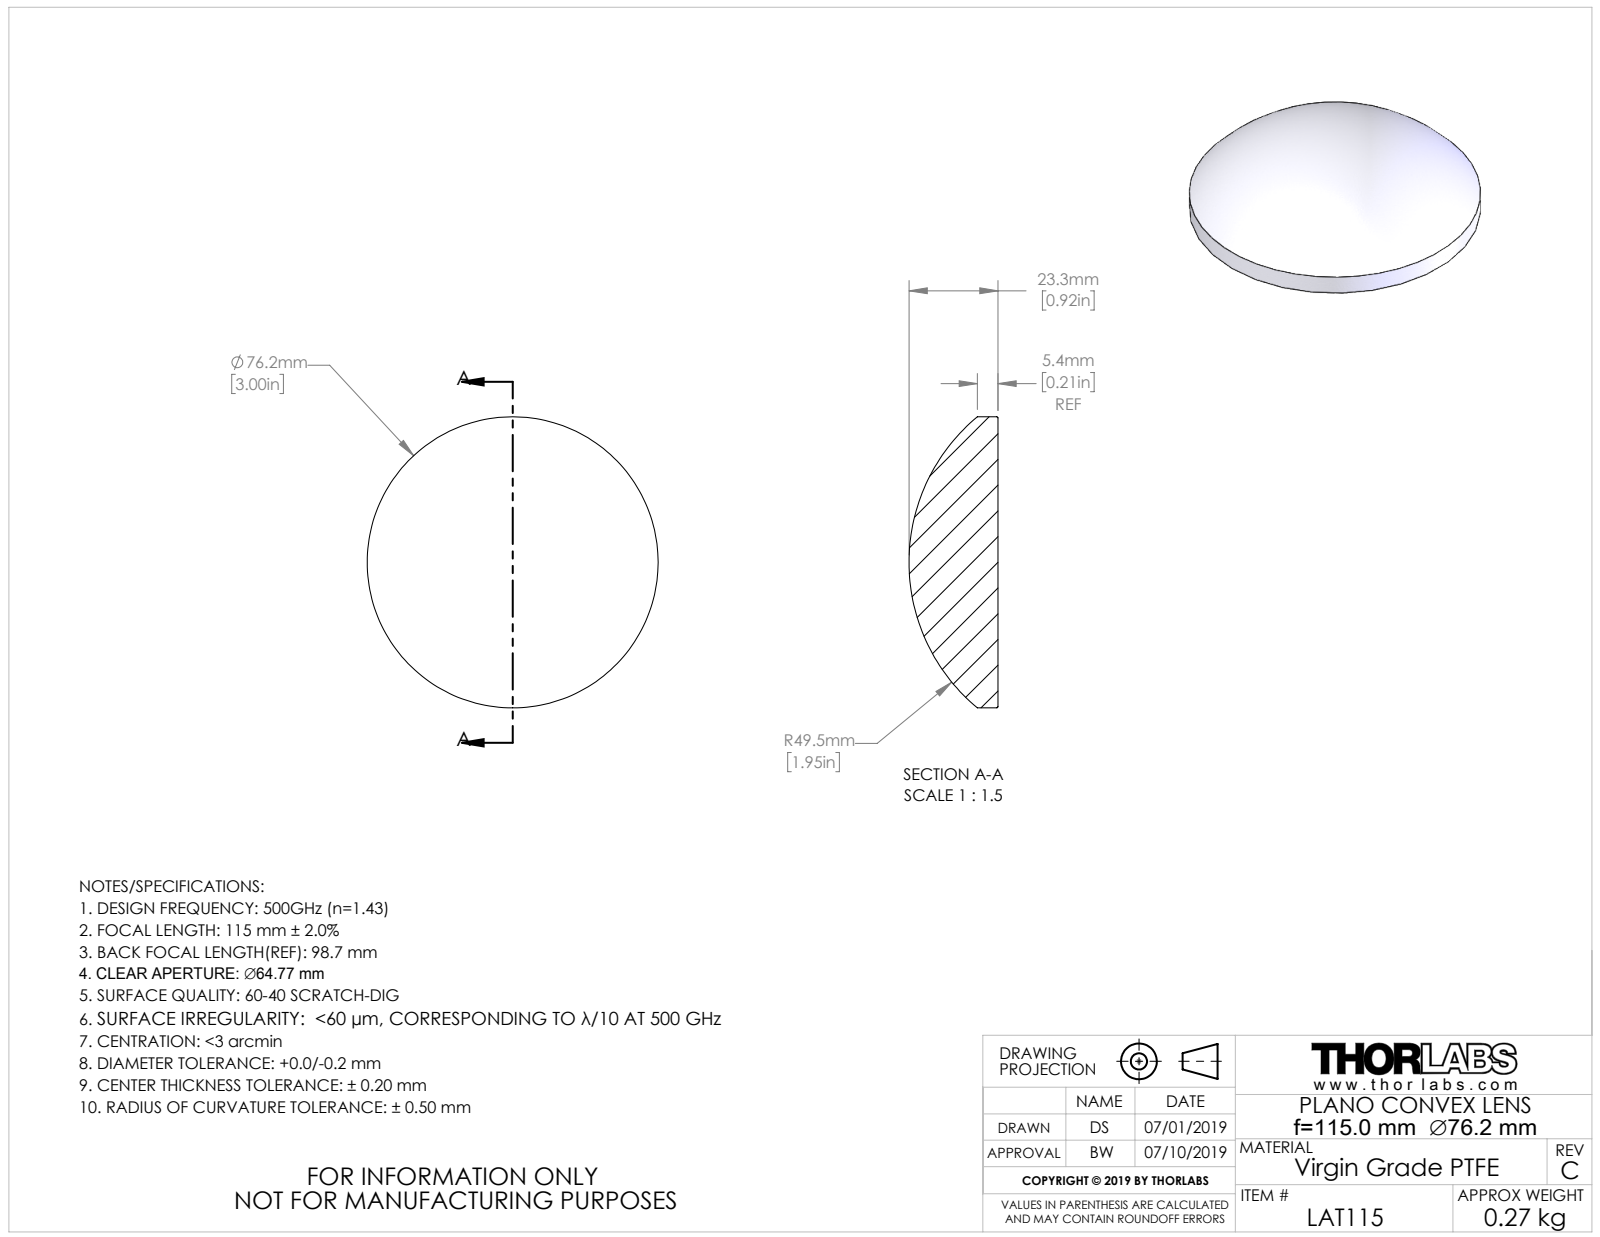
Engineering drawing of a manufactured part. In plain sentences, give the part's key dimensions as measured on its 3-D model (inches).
The part is named "TTN041006-E0W". Its 3-D file was written by "SolidWorks 2018 (CONFIG_CONTROL_DESIGN)". It is 1 solid with 7 faces: 1 planar, 2 cylindrical and 4 other. Overall it measures 3 by 3 by 0.917 inches. Its volume is 4.175 cubic inches and its surface area 17.65 square inches. Round bosses or shafts: 1 of diameter 3.
